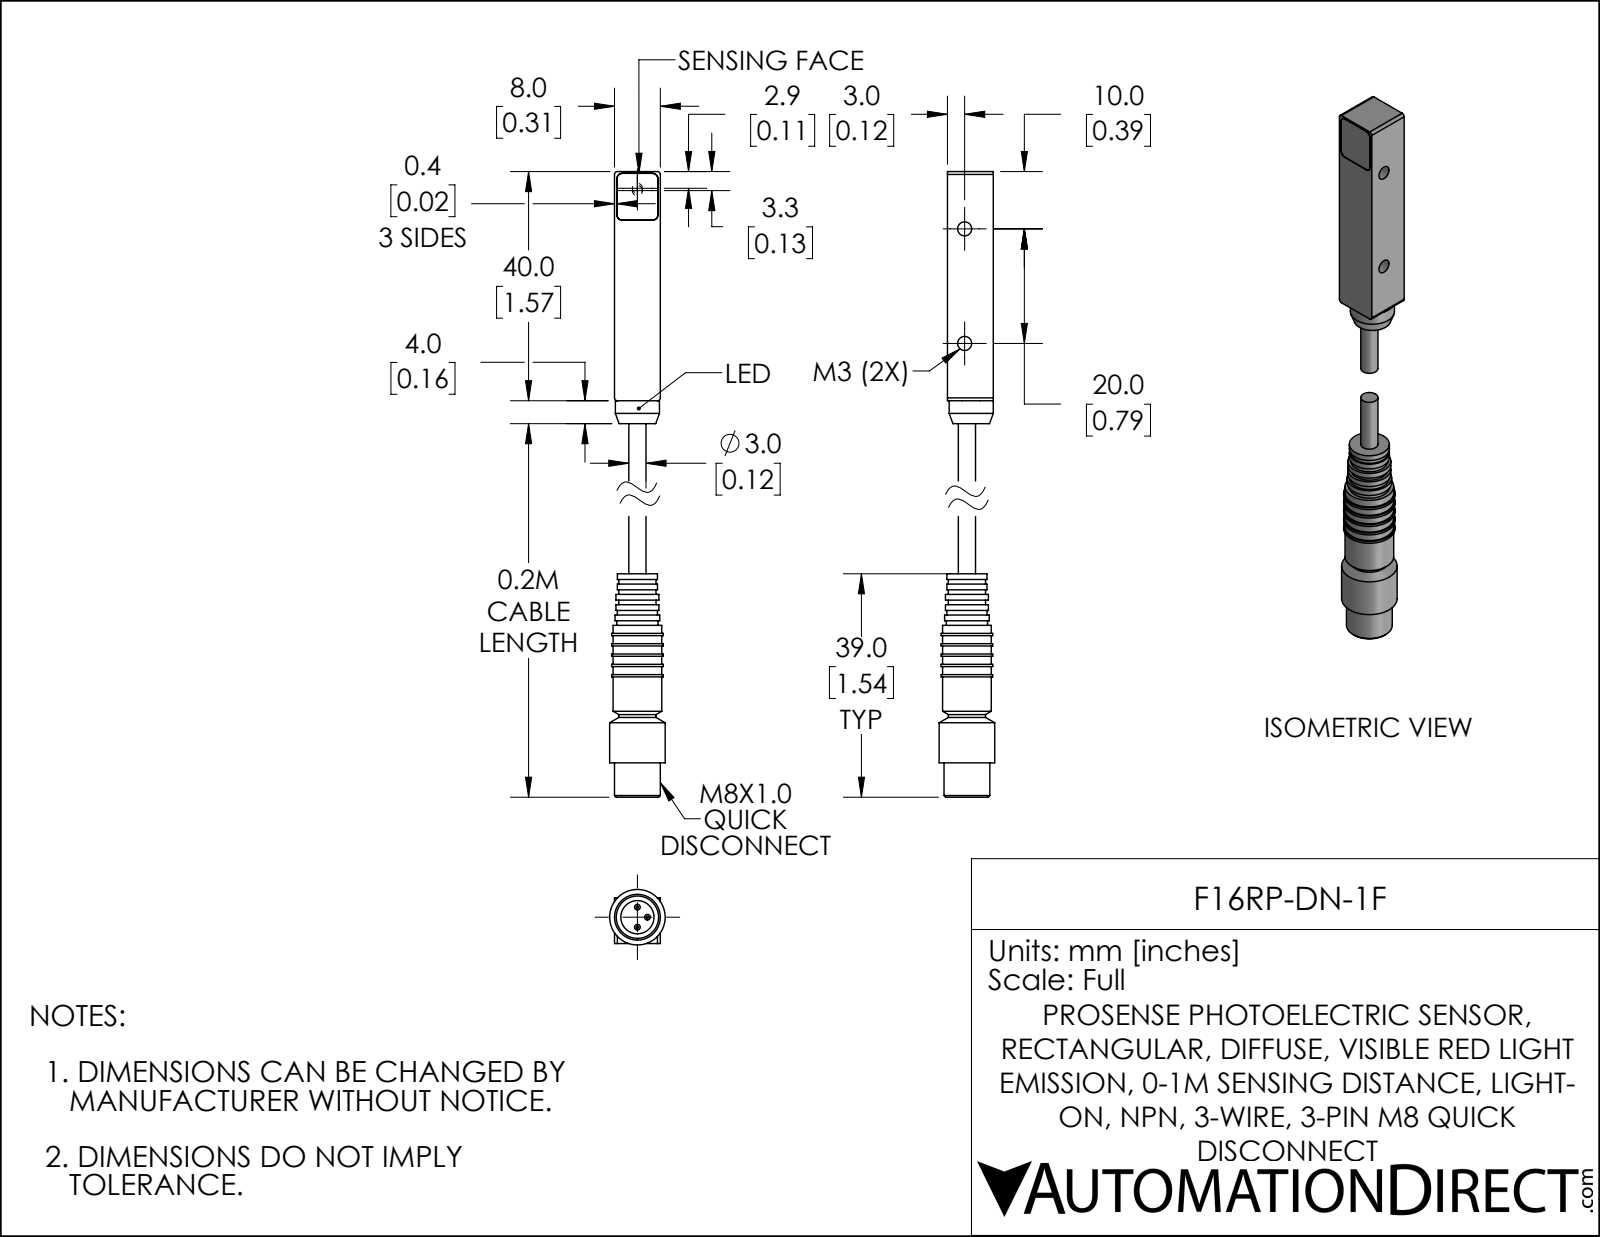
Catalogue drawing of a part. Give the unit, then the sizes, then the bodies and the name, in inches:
Units: inches
Overall size (bounding box): 4.331 × 0.382 × 0.382
Round holes (diameter × count): ⌀0.097 ×2, ⌀0.228 ×1
Round bosses / shafts (diameter × count): ⌀0.039 ×3, ⌀0.382 ×1, ⌀0.354 ×1, ⌀0.335 ×1, ⌀0.315 ×1, ⌀0.307 ×1, ⌀0.303 ×1, ⌀0.295 ×1
Partial cylindrical surfaces — rounded edges, fillets, slot ends (radius × count): R0.02 ×4, R0.039 ×4, R0.039 ×4
Main face-to-face distances: 0.315, 0.071, 0.142, 0.039, 0.354, 1.732, 2.796, 2.402, 0.213, 1.063
Hole centre spacings: 0.787
Volume: 0.293 in³ · Surface area: 5.017 in²
Bodies: 2 solids, 102 faces (50 planar, 45 cylindrical, 7 other)
Part name (STEP PRODUCT): F16RP-DN-1F; F16RP-DN-1F_2; F16RP-DN-1F_1
STEP written by: SolidWorks 2019 (AUTOMOTIVE_DESIGN)
